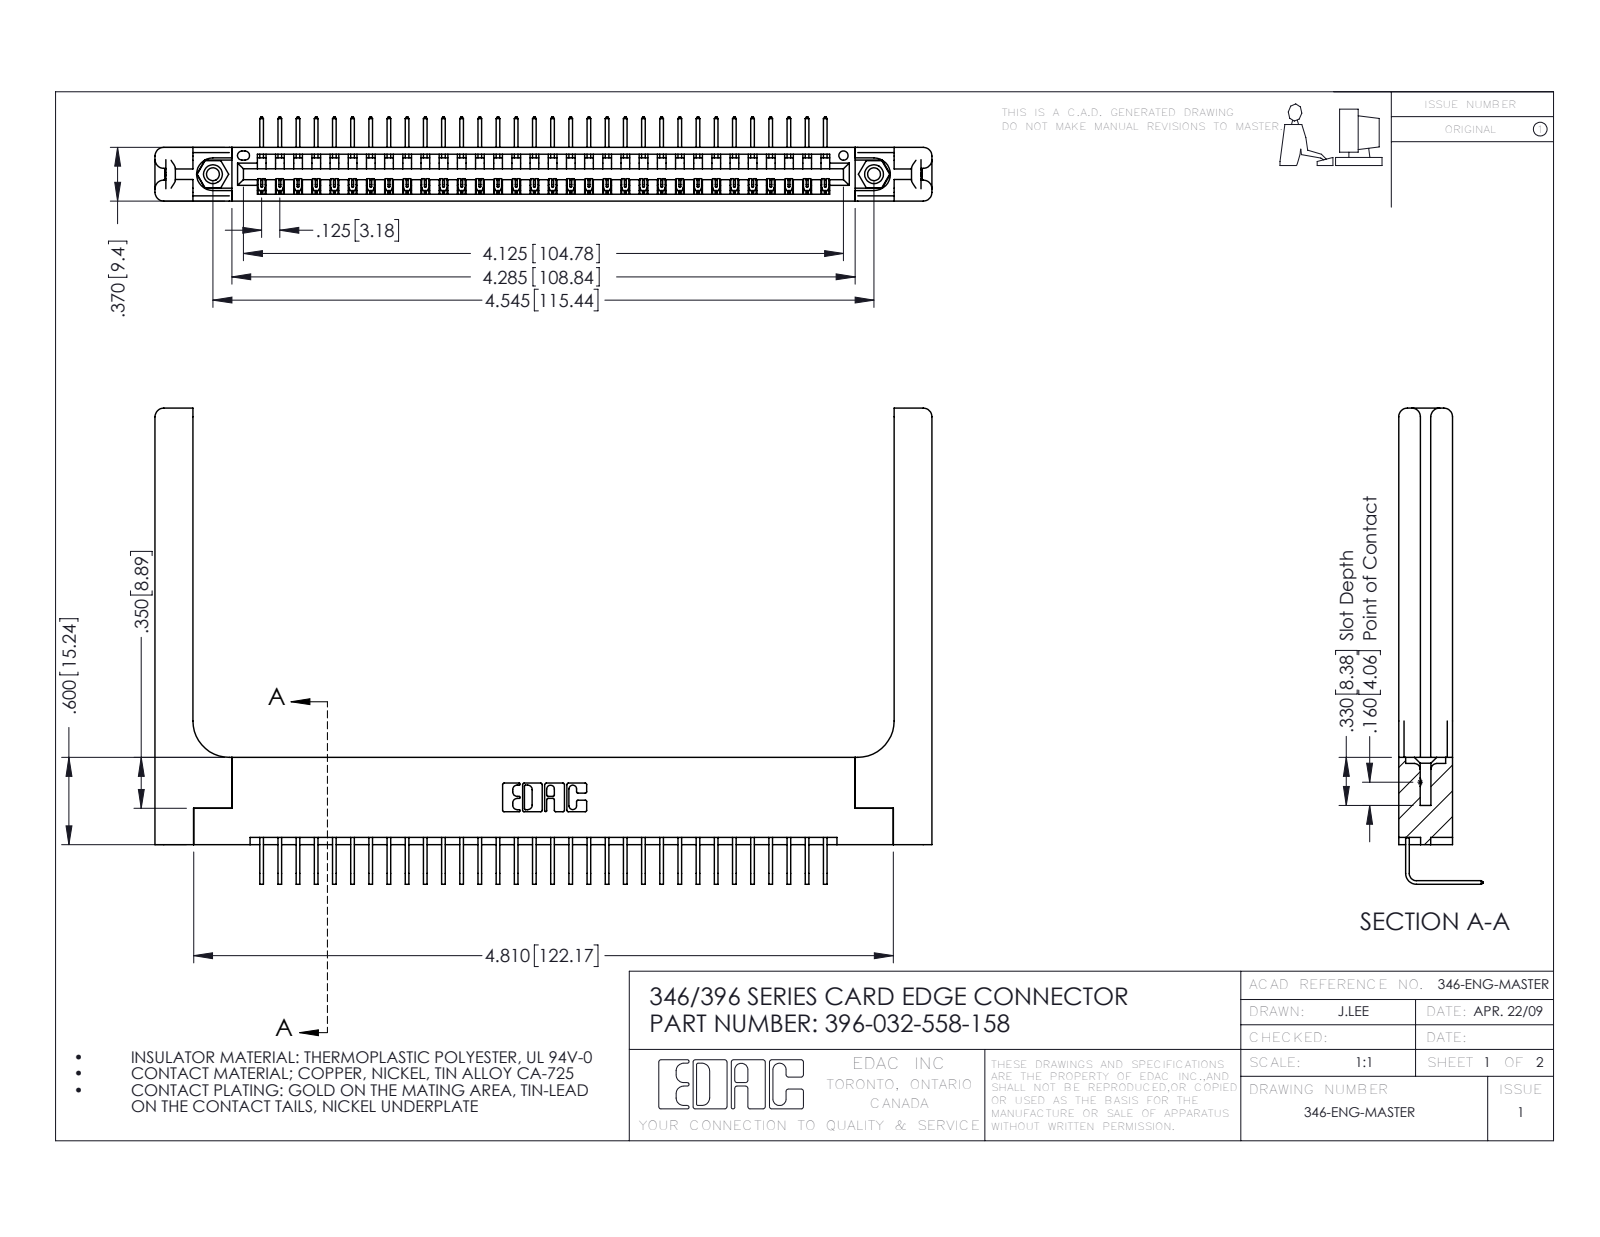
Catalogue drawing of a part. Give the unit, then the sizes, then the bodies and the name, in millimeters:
Units: millimetres
Overall size (bounding box): 135.7 × 83.1 × 14.7
Round holes (diameter × count): ⌀2.3 ×2, ⌀3.2 ×2, ⌀4 ×2, ⌀1.6 ×1
Round bosses / shafts (diameter × count): ⌀3.9 ×2
Partial cylindrical surfaces — rounded edges, fillets, slot ends (radius × count): R0.2 ×64, R0.3 ×22, R1.5 ×16, R0.2 ×6, R0.8 ×6, R0.7 ×3, R0.8 ×2, R0.8 ×2
Main face-to-face distances: 9.4, 8.2, 1.2, 1.8, 3.8, 3.8, 6.4, 0.6, 7.6, 5.6
Hole centre spacings: 6.2, 110.2, 115.4
Volume: 20 550 mm³ · Surface area: 21 970 mm²
Bodies: 37 solids, 2298 faces (1568 planar, 670 cylindrical, 60 other)
Part name (STEP PRODUCT): 345-292-001_558 Tail - 2; 346-220-058_345-220-058; 345-250-001_345-250-001-102; 346 Part_Flush Mounting Lugs - 0.156 Dia-TH (+1 more)
STEP written by: SolidWorks 2016 (CONFIG_CONTROL_DESIGN)
